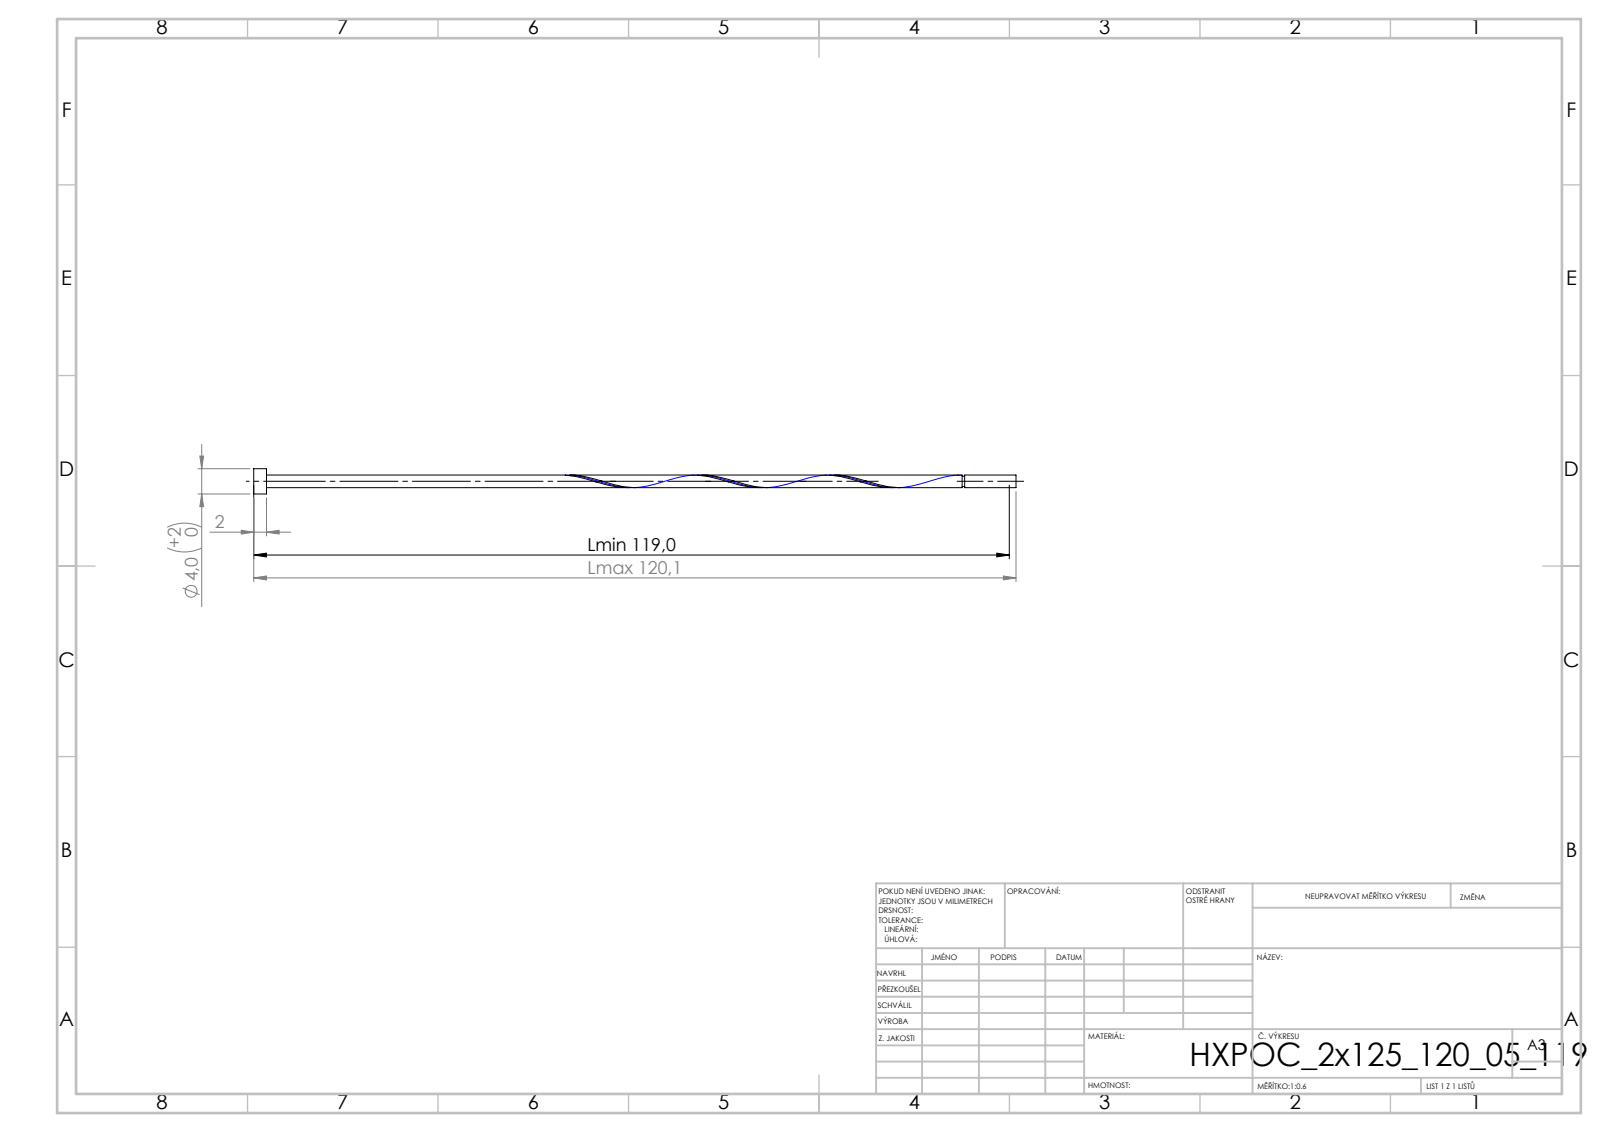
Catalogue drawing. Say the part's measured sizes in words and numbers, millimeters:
Its 3-D file was written by "SolidWorks 2019 (CONFIG_CONTROL_DESIGN)". It is 1 solid with 16 faces: 6 planar, 9 cylindrical and 1 other. Overall it measures 120.05 by 4 by 4 millimeters. Its volume is 479 cubic millimeters and its surface area 1 069 square millimeters. Round bosses or shafts: 1 of diameter 4, 1 of diameter 2, 1 of diameter 1.6. The main face-to-face distances are 2, 120.05, 118.05, 111.96, 109.96, 8.09, 111.56, 109.56, 0.4, 8.49.
